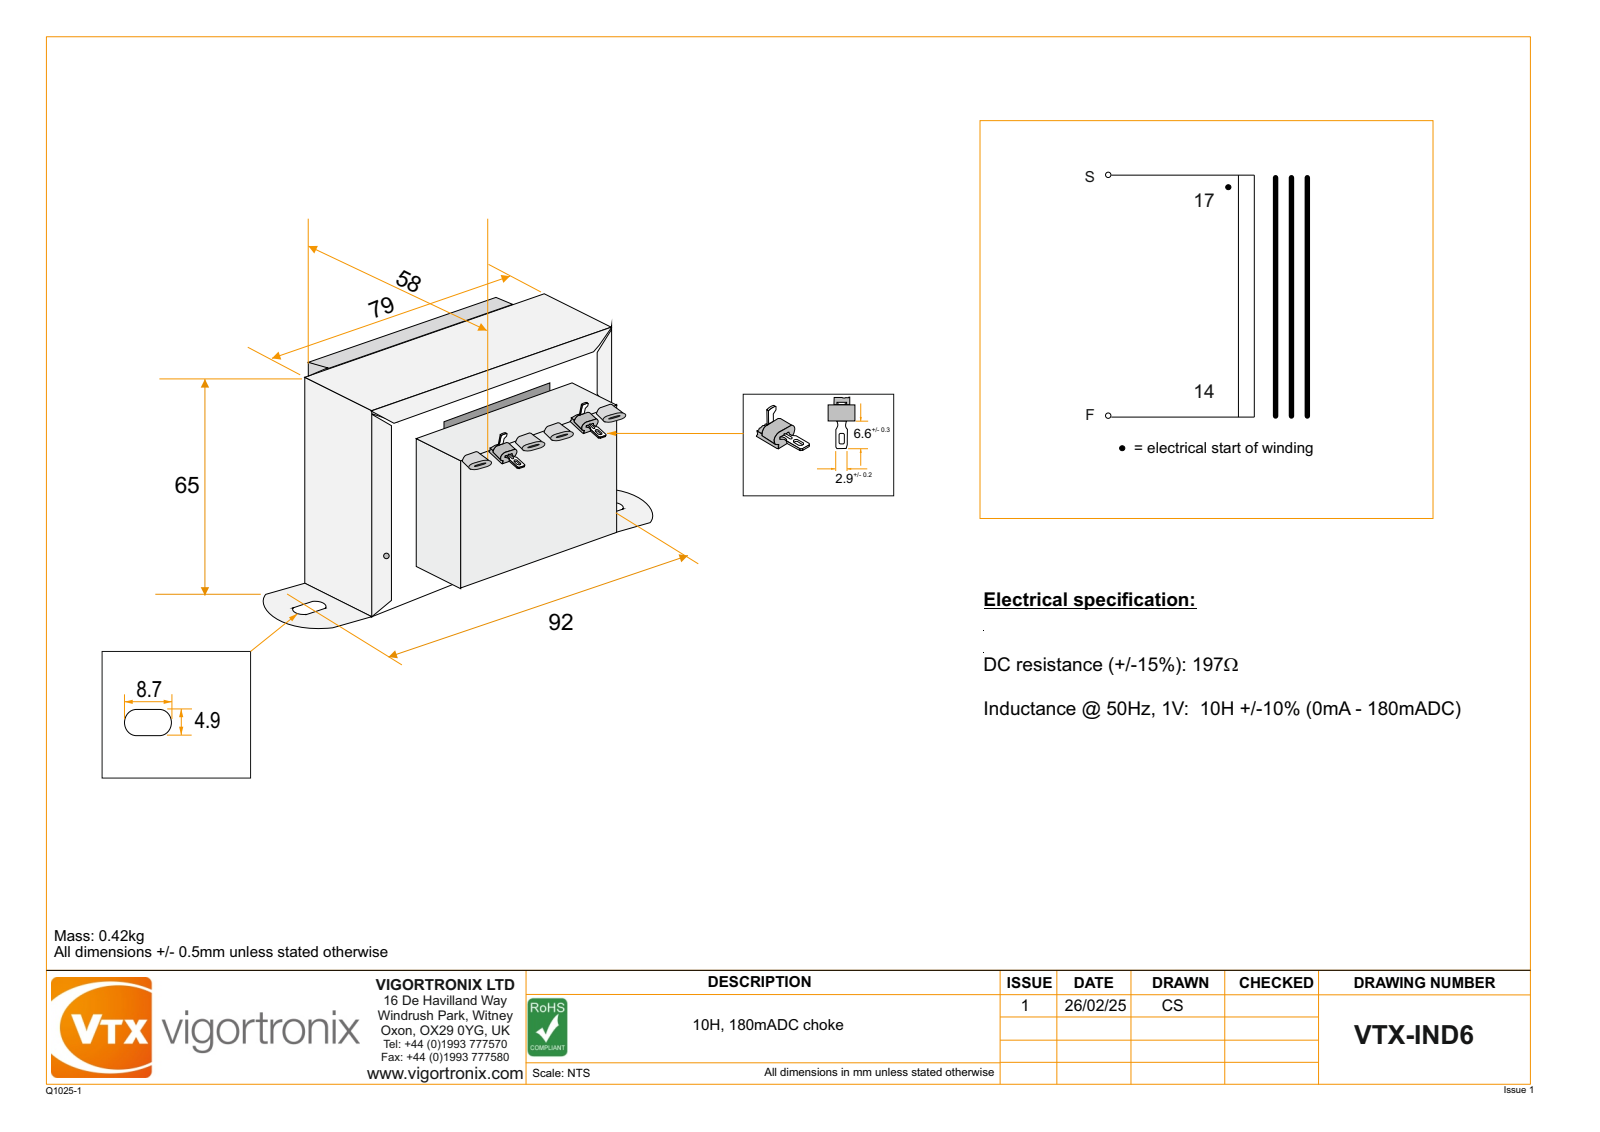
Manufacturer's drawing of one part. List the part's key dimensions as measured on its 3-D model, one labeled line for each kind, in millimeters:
Part name (STEP PRODUCT): Terminal Pin 902 Bent; VTX-IND6; Clamp EIUK29; 29 x 1 INCH S0200 Bobbin (+3 more)
STEP written by: SolidWorks 2024 (AUTOMOTIVE_DESIGN)
Units: millimetres
Bodies: 133 solids, 1878 faces (1718 planar, 148 cylindrical, 12 other)
Overall size (bounding box): 107.9 × 65 × 62.1
Volume: 168 312 mm³ · Surface area: 561 328 mm²
Partial cylindrical surfaces — rounded edges, fillets, slot ends (radius × count): R1.5 ×24, R1 ×22, R0.63 ×18, R0.1 ×12, R1.8 ×10, R0.25 ×5, R2.45 ×4, R3 ×4
Main face-to-face distances: 0.4, 0.8, 1.2, 1.6, 2, 2.4, 2.8, 3.2, 3.6, 4
